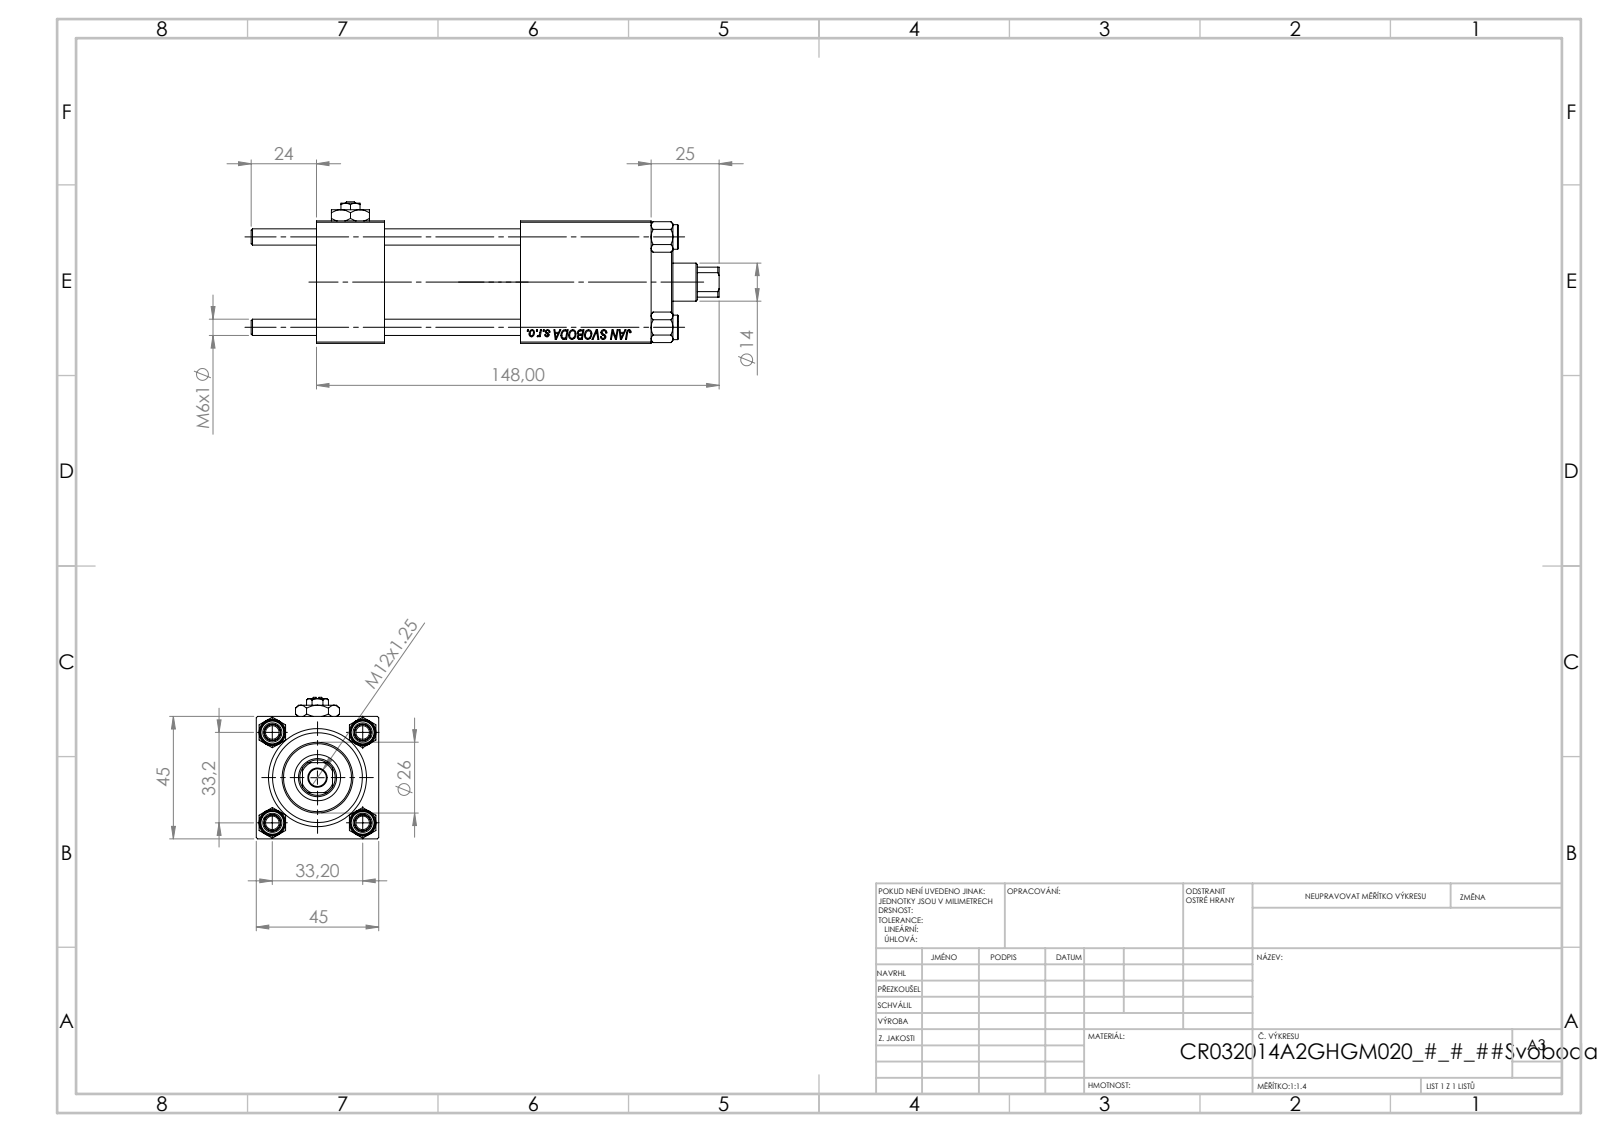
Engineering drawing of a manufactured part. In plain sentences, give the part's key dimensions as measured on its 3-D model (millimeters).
The part is named "NUT_M5; V215_VC_A; Zatka_pro_OIL_PORT; CR025_012_A_0_G_A_G_M_020_+#_##_TYCINKA (+2 more)". Its 3-D file was written by "SolidWorks 2019 (CONFIG_CONTROL_DESIGN)". It is 12 solids with 1184 faces: 542 planar, 84 cylindrical and 558 other. Overall it measures 172 by 52 by 45 millimeters. Its volume is 197 462 cubic millimeters and its surface area 73 903 square millimeters. Round holes: 4 of diameter 6, 2 of diameter 7, 2 of diameter 13.16, 2 of diameter 20, 1 of diameter 6.5, 1 of diameter 14, 1 of diameter 17, 1 of diameter 24, 1 of diameter 32, 1 of diameter 33. Round bosses or shafts: 4 of diameter 9, 1 of diameter 38, 1 of diameter 26. Partial cylindrical surfaces (rounded edges, fillets, slot ends): 1 of radius 6.5. The main face-to-face distances are 45, 25, 123, 98, 50, 75, 48, 94.3, 69.3, 19.3. The hole center spacings are 23.48, 33.2, 46.95, 75.5.
